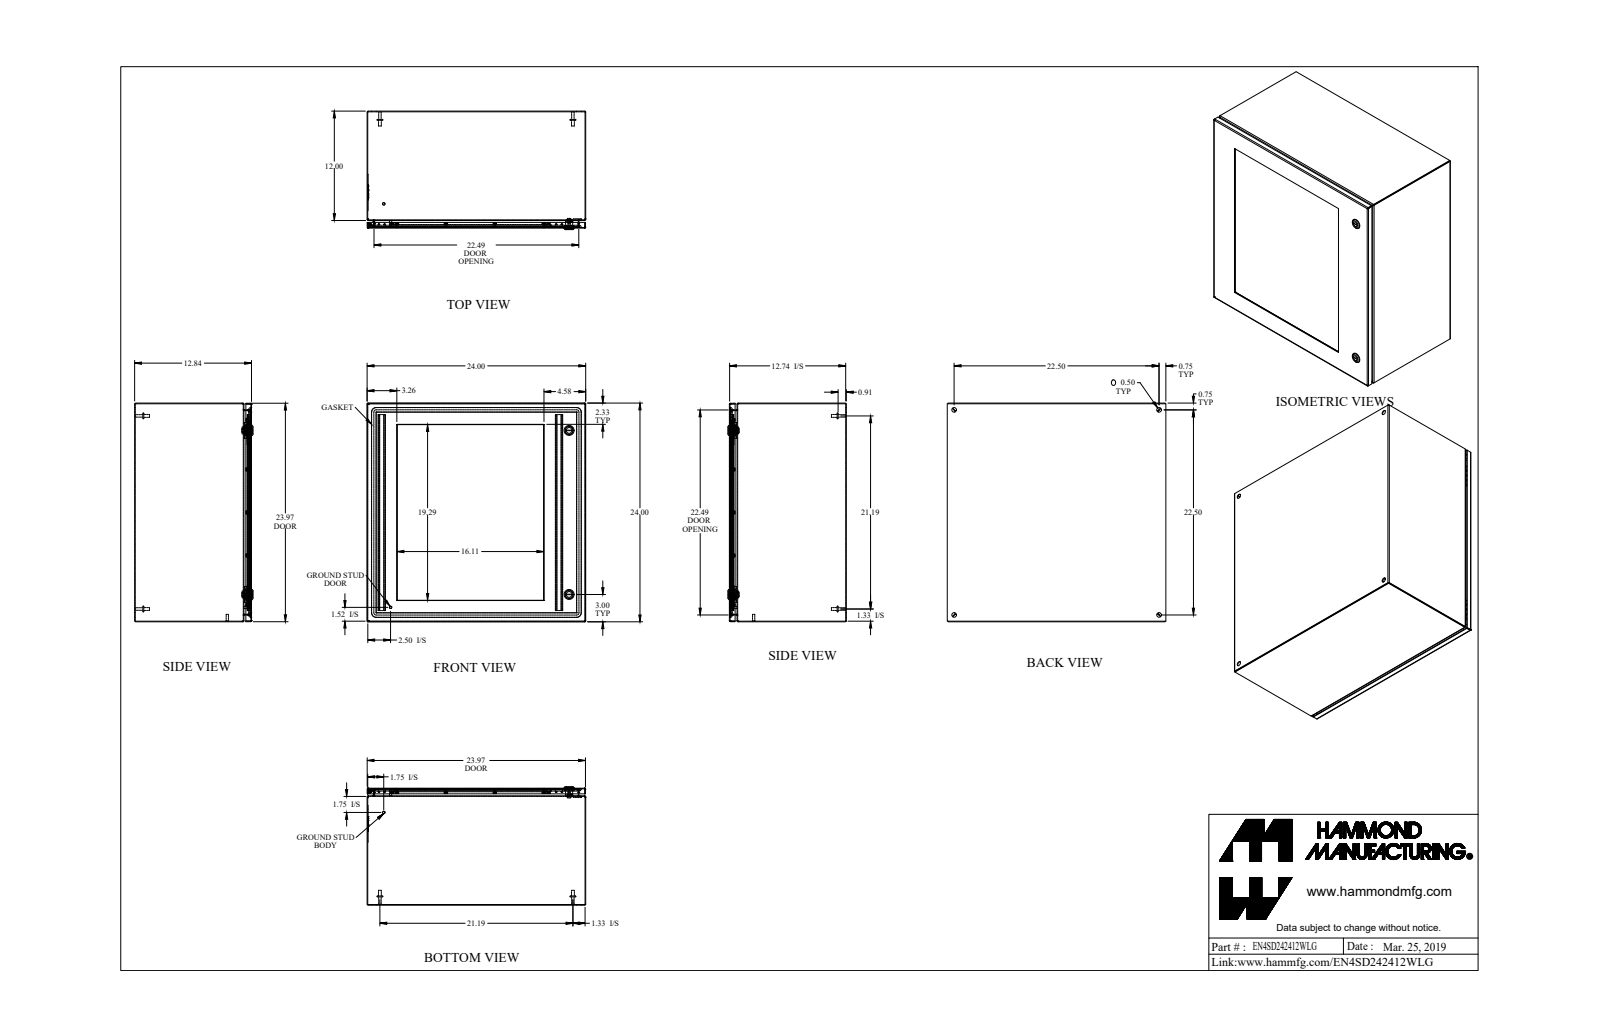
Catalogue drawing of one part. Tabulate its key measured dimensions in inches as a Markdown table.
| quantity | value |
| --- | --- |
| part name | EN4SD242412WLG |
| STEP written by | SolidWorks 2019 (AUTOMOTIVE_DESIGN) |
| units | inches |
| bodies | 74 solids, 1435 faces (740 planar, 441 cylindrical, 254 other) |
| overall size | 24 × 24 × 12.997 |
| volume | 258.1 in³ |
| surface area | 5 655 in² |
| round holes (diameter × count) | 0.13 × 18, 0.25 × 18, 0.5 × 4, 0.232 × 2, 0.625 × 2, 0.785 × 2, 0.172 × 1, 0.24 × 1, 0.242 × 1 |
| round bosses / shafts (diameter × count) | 0.226 × 19, 0.368 × 18, 0.164 × 18, 0.625 × 4, 0.313 × 4, 0.27 × 4, 1.1 × 2, 0.525 × 2 |
| partial cylindrical surfaces (radius × count) | 0.036 × 14, 0.108 × 14, 0.043 × 12, 0.081 × 12, 0.125 × 12, 0.312 × 12, 0.1 × 8, 0.006 × 4 |
| main face-to-face distances | 0.072, 23.928, 12.765, 12.693, 23.856, 24, 12.443, 0.25, 12.515, 0.322 |
| hole center spacings | 5.372, 17.781, 4.719, 19.57, 21.03, 5.372, 9.437, 10.743 |
